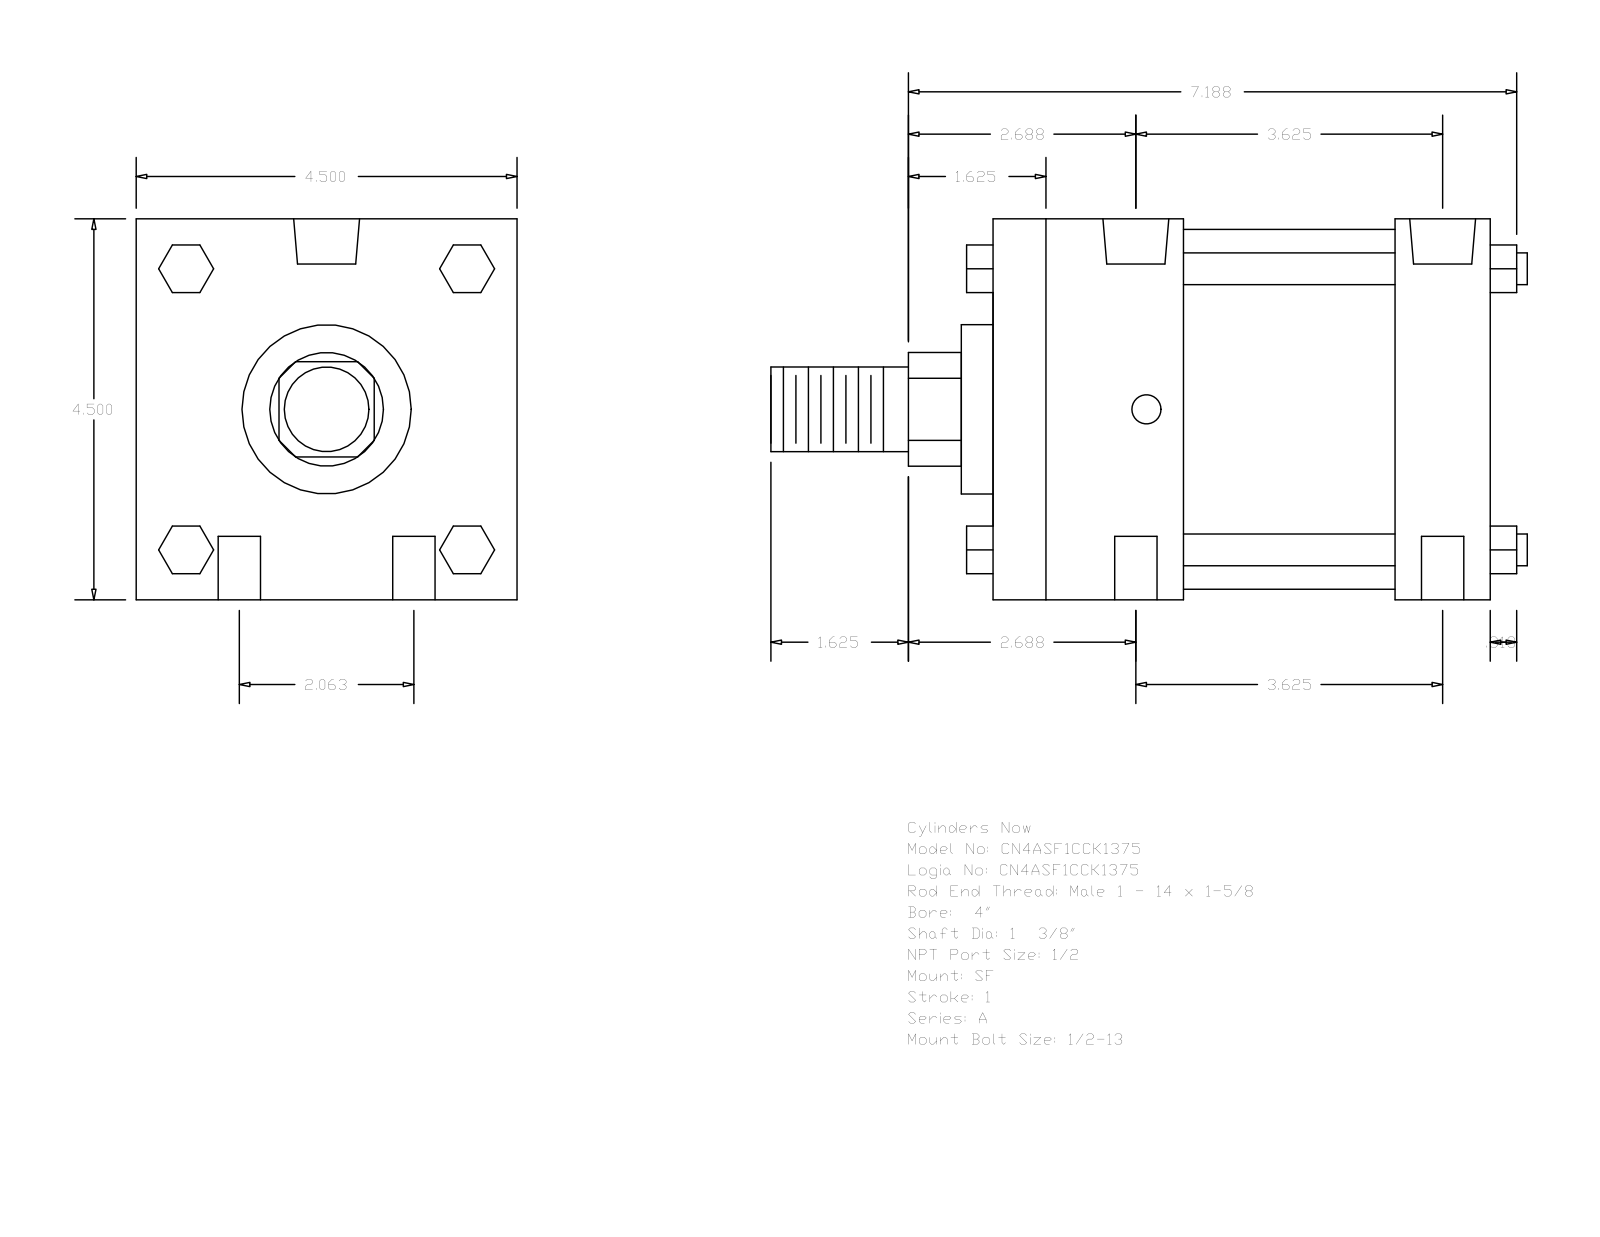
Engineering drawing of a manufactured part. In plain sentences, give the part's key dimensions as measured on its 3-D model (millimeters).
The part is named "A_SF__0400_1.375". Its 3-D file was written by "GSSL Pune (CONFIG_CONTROL_DESIGN)". It is 0 solids with 124 faces: 94 planar, 30 cylindrical and 0 other. Overall it measures 227.01 by 114.3 by 114.3 millimeters. Round holes: 4 of diameter 12.7, 2 of diameter 8.73, 2 of diameter 19.77. Round bosses or shafts: 4 of diameter 9.53, 1 of diameter 107.95, 1 of diameter 50.8, 1 of diameter 34.92, 1 of diameter 25.4. Partial cylindrical surfaces (rounded edges, fillets, slot ends): 1 of radius 17.06. The main face-to-face distances are 114.3, 149.22, 57.15, 120.65, 28.57, 63.5, 92.07, 66.67, 14.29, 9.52. The hole center spacings are 26.19, 95.73, 92.08, 52.38, 105.94, 85.72.
